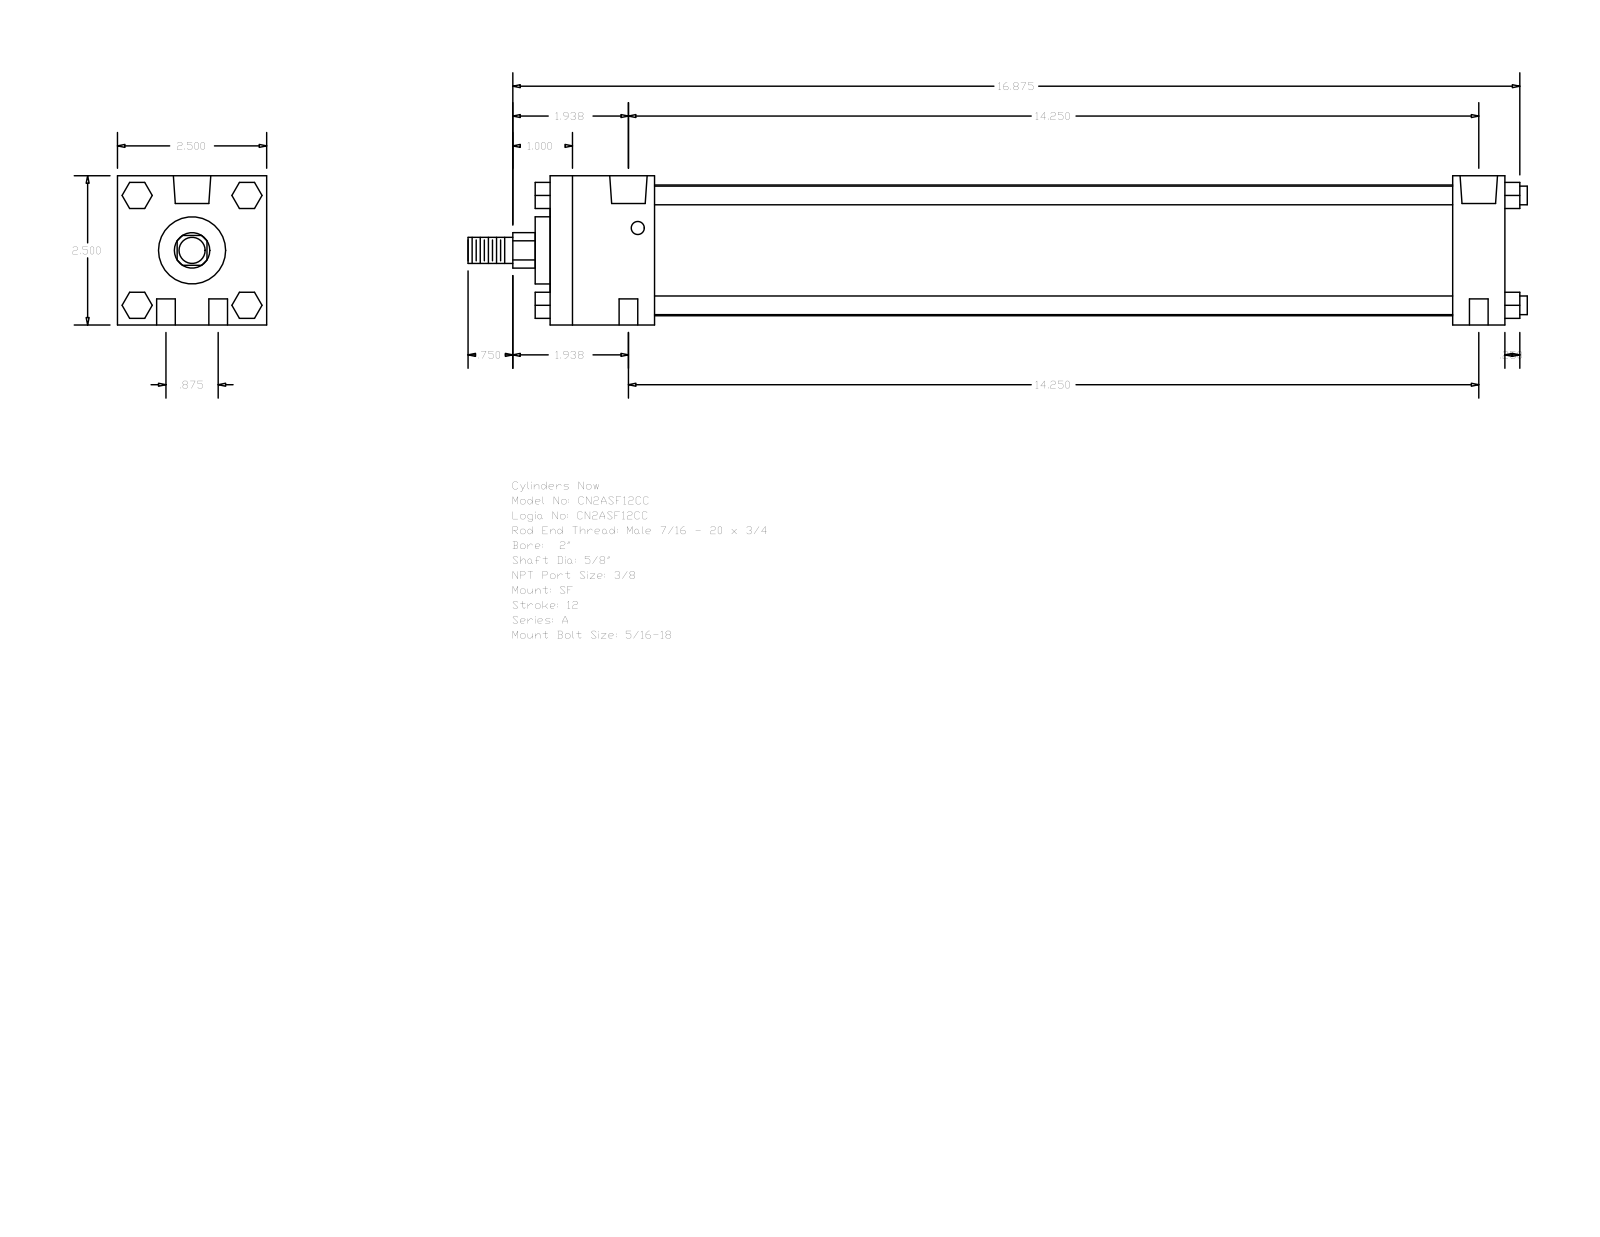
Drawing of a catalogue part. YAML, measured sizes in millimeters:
part_name: "A_SF__0200_0.625"
step_written_by: "GSSL Pune (CONFIG_CONTROL_DESIGN)"
units: millimeters
bodies: {solids: 0, faces: 124, planar: 94, cylindrical: 30, other: 0}
overall_size: [450.85, 63.5, 63.5]
round_holes:
  - {diameter: 7.94, count: 4}
  - {diameter: 5.56, count: 2}
  - {diameter: 15.93, count: 2}
round_bosses_or_shafts:
  - {diameter: 7.94, count: 4}
  - {diameter: 55.63, count: 1}
  - {diameter: 28.57, count: 1}
  - {diameter: 15.88, count: 1}
  - {diameter: 11.11, count: 1}
partial_cylinders:
  - {radius: 7.54, count: 1}
face_to_face_distances: [63.5, 406.39, 384.17, 22.22, 44.45, 339.72, 361.94, 6.35, 412.74, 50.8]
hole_center_spacings: [11.11, 362.12, 361.95, 22.22, 362.63, 354]
